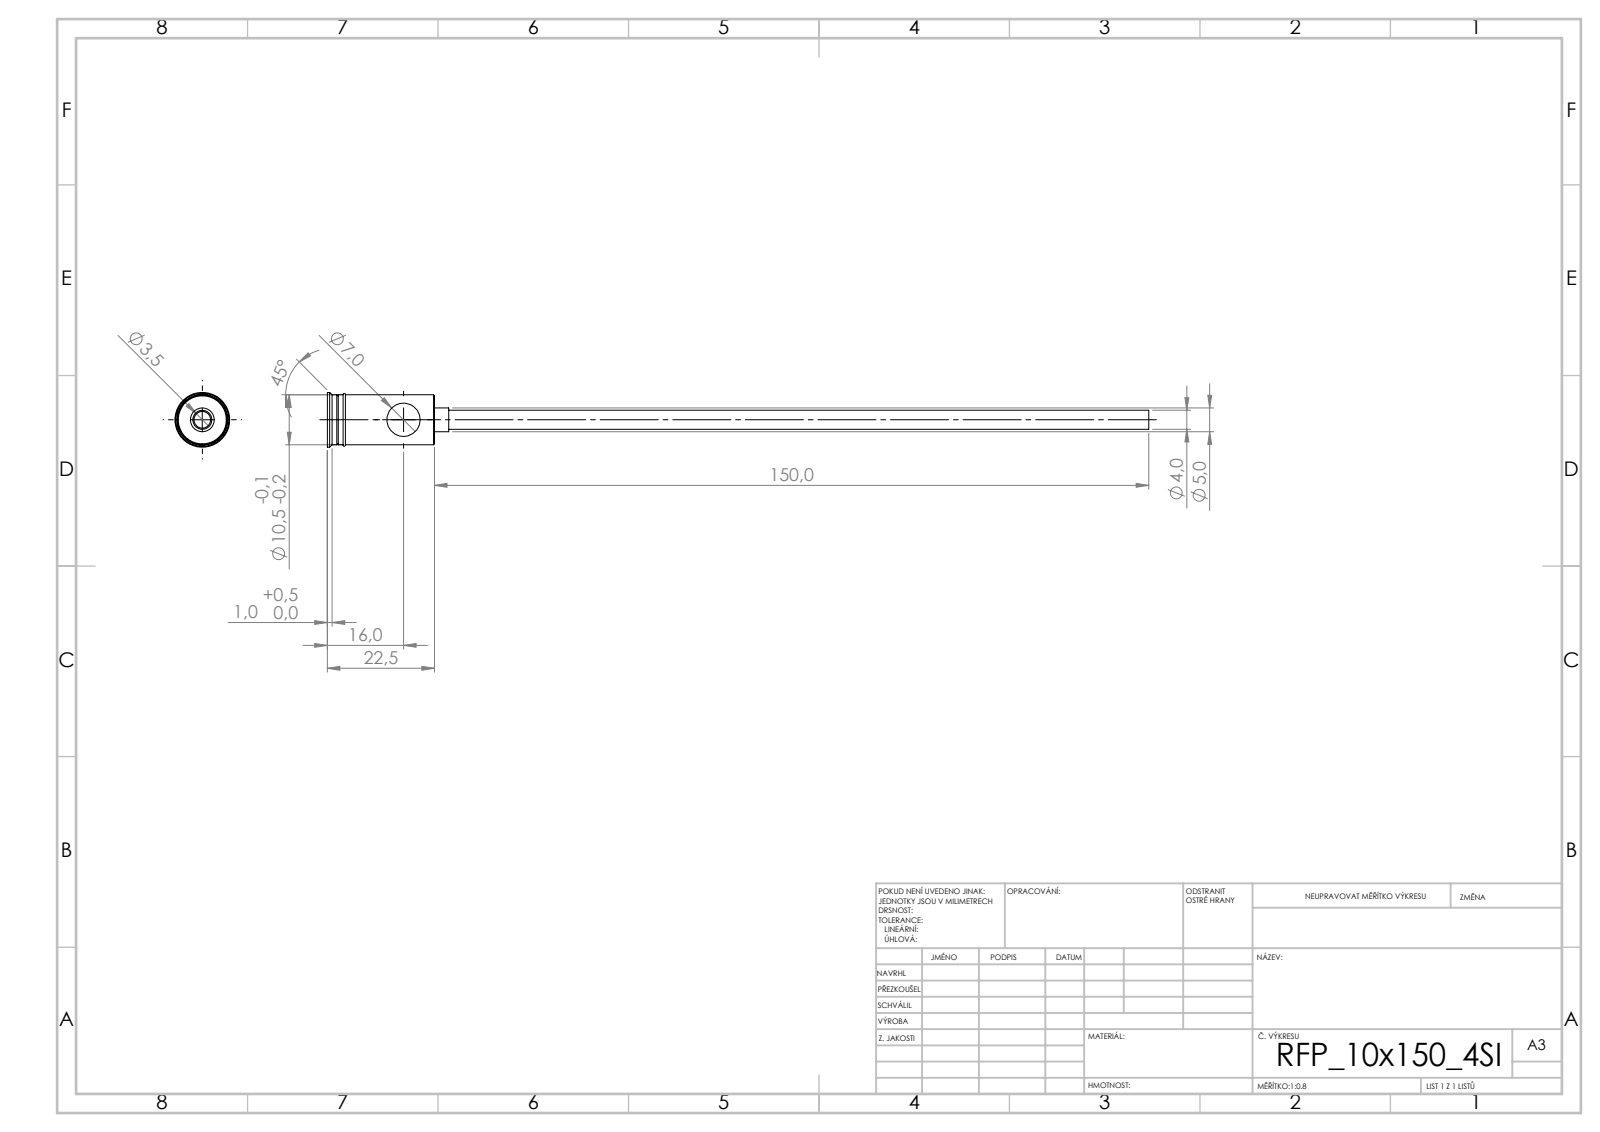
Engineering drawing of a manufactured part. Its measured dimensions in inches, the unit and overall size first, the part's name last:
Units: inches
Overall size (bounding box): 6.791 × 0.453 × 0.453
Round holes (diameter × count): ⌀0.138 ×1, ⌀0.276 ×1
Round bosses / shafts (diameter × count): ⌀0.453 ×1, ⌀0.413 ×1, ⌀0.197 ×1, ⌀0.157 ×1
Main face-to-face distances: 0.886, 0.807, 0.079, 0.232, 0.795, 0.091, 0.118, 0.913, 0.925, 1.004
Volume: 0.119 in³ · Surface area: 7.26 in²
Bodies: 1 solid, 44 faces (20 planar, 16 cylindrical, 8 other)
STEP written by: SolidWorks 2019 (CONFIG_CONTROL_DESIGN)
